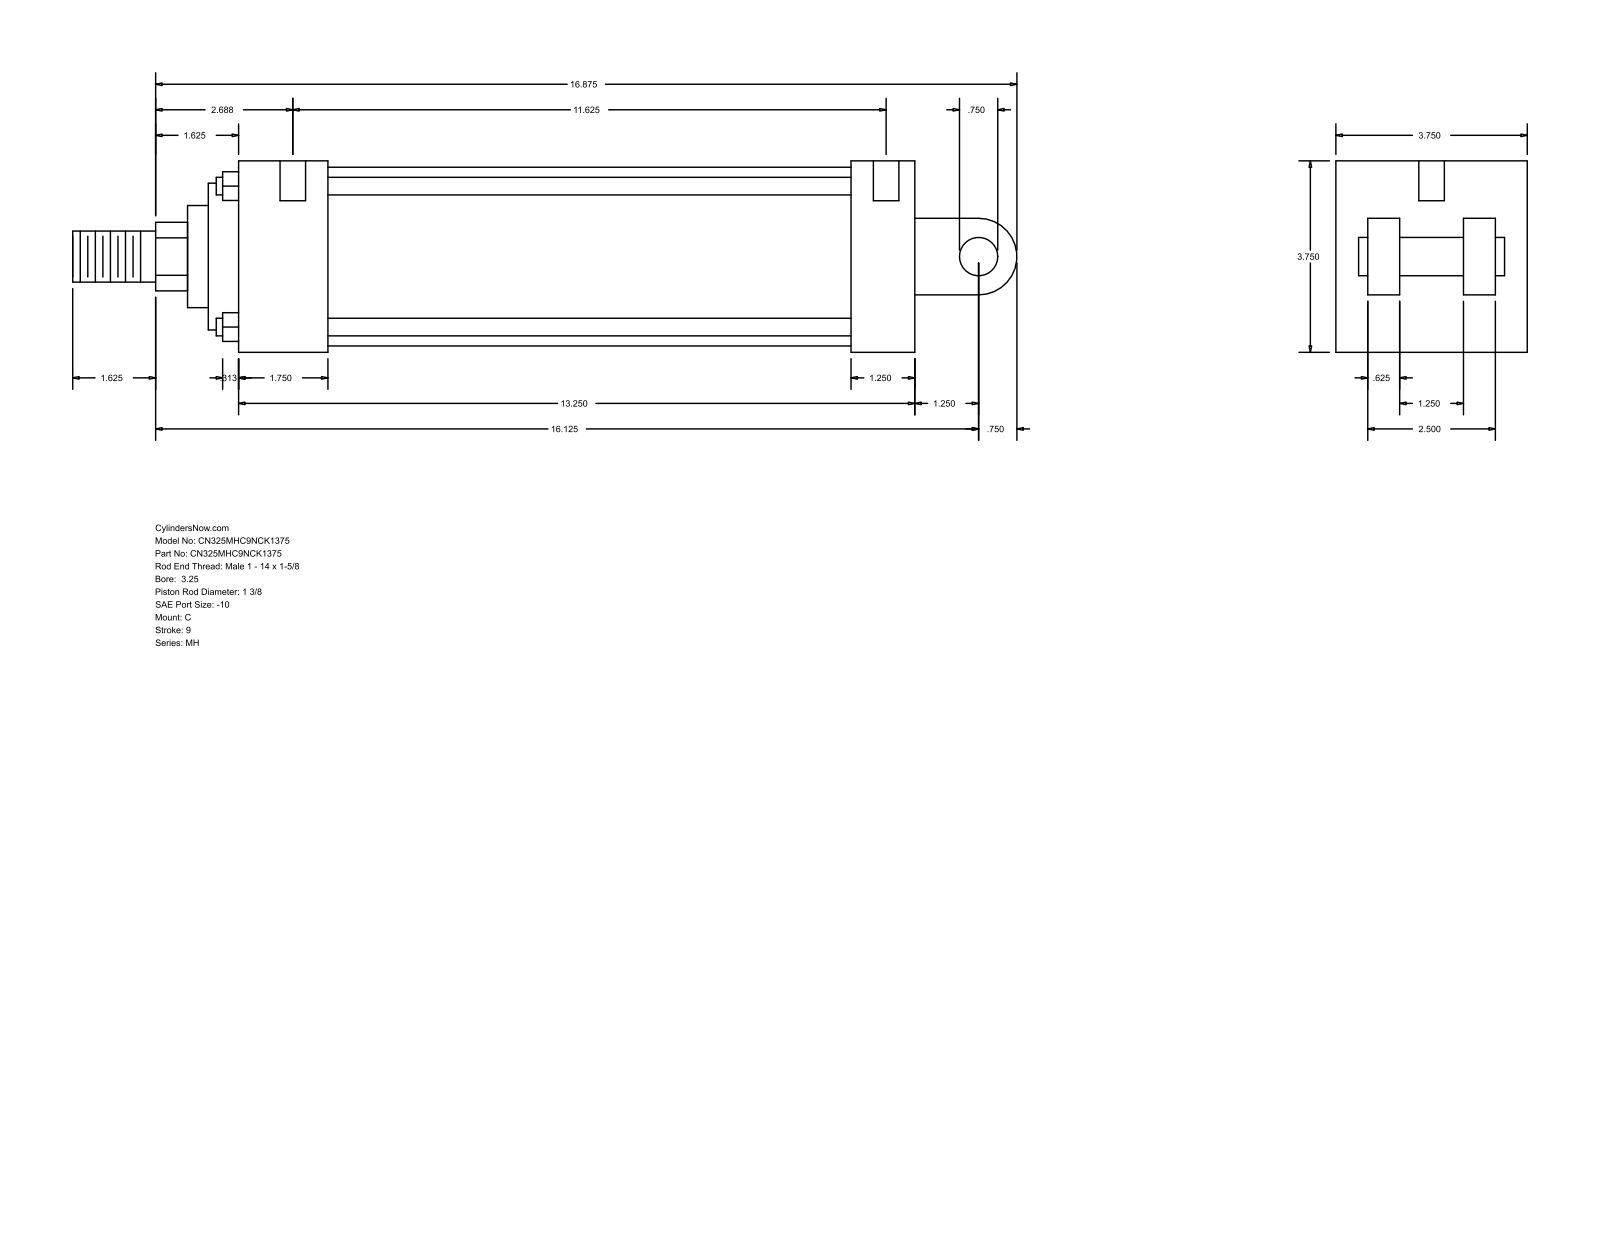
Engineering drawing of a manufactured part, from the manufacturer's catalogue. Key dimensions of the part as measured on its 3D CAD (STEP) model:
Part name (STEP PRODUCT): MH_C__0325_1.375
STEP written by: GSSL Pune (CONFIG_CONTROL_DESIGN)
Units: millimetres
Bodies: 0 solids, 101 faces (71 planar, 30 cylindrical, 0 other)
Overall size (bounding box): 469.9 × 95.25 × 95.25
Round holes (diameter × count): ⌀5.56 ×4, ⌀12.7 ×2
Round bosses / shafts (diameter × count): ⌀8.76 ×4, ⌀88.9 ×1, ⌀73.03 ×1, ⌀50.8 ×1, ⌀34.92 ×1, ⌀25.4 ×1, ⌀19.05 ×1
Partial cylindrical surfaces — rounded edges, fillets, slot ends (radius × count): R17.06 ×1, R19.05 ×1
Main face-to-face distances: 95.24, 15.87, 63.5, 336.55, 79.37, 31.74, 47.63, 44.45, 304.8, 260.35
Hole centre spacings: 301.63, 1.59, 4.76, 295.28, 296.87, 300.04
